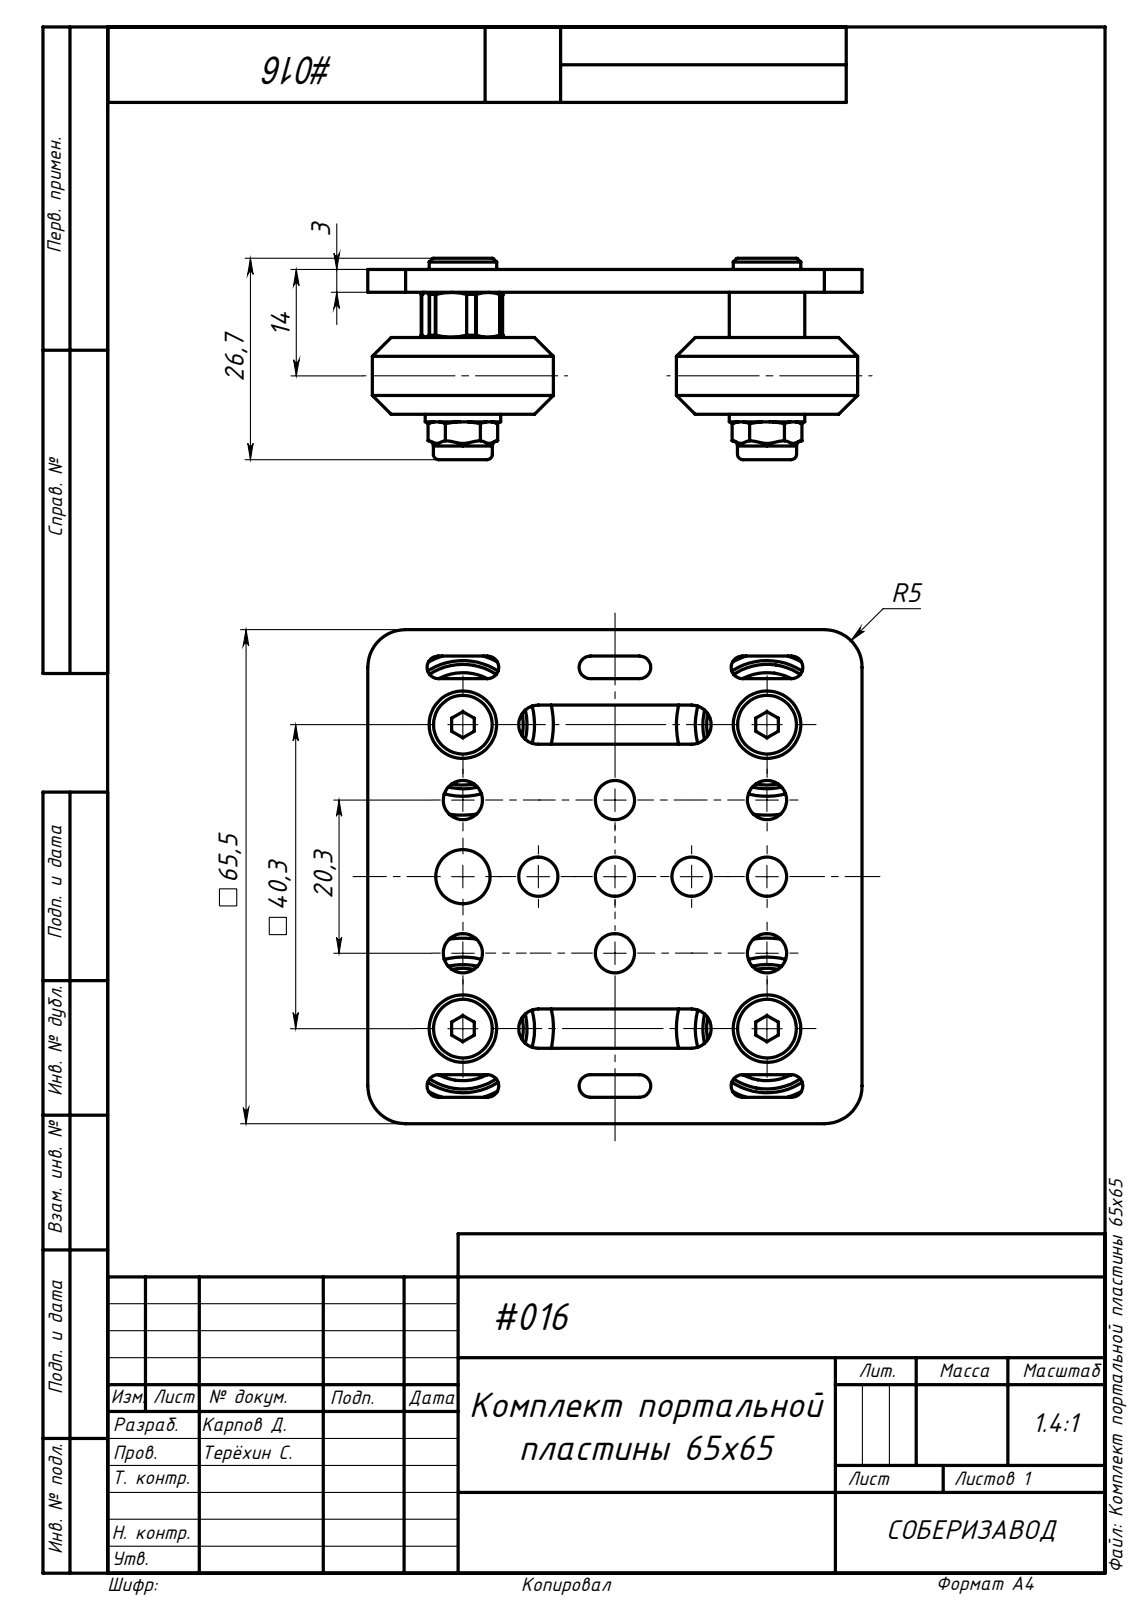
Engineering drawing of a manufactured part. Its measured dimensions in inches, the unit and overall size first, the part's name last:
Units: inches
Overall size (bounding box): 2.579 × 2.579 × 1.051
Round holes (diameter × count): ⌀0.205 ×14, ⌀0.163 ×4, ⌀0.197 ×4, ⌀0.203 ×4, ⌀0.543 ×4, ⌀0.551 ×4, ⌀0.63 ×4, ⌀0.283 ×3
Round bosses / shafts (diameter × count): ⌀0.945 ×4, ⌀0.394 ×4, ⌀0.352 ×4, ⌀0.339 ×4, ⌀0.308 ×4, ⌀0.276 ×2
Partial cylindrical surfaces — rounded edges, fillets, slot ends (radius × count): R0.008 ×28, R0.059 ×12, R0.102 ×4, R0.197 ×4
Main face-to-face distances: 0.118, 0.205, 0.014, 0.183, 0.236, 0.638, 0.756, 0.402, 0.354, 0.197
Hole centre spacings: 0.793, 0.4, 0.885, 0.888, 1.433, 1.587, 0.394, 1.193
Volume: 1.882 in³ · Surface area: 43.43 in²
Bodies: 33 solids, 646 faces (216 planar, 286 cylindrical, 144 other)
Part name (STEP PRODUCT): A201 Дистанционная втулка 5х6 мм_00; A211 Высокоточная дистанционная шайба 5 мм_00; A195-Standartnyy-ekstsentrik-6-mm_-dlya-vinta-M5_podrobnaya-model__00; Комплект портальной пластины 65x65 (+4 more)
STEP written by: SolidWorks 2021 (AUTOMOTIVE_DESIGN)
